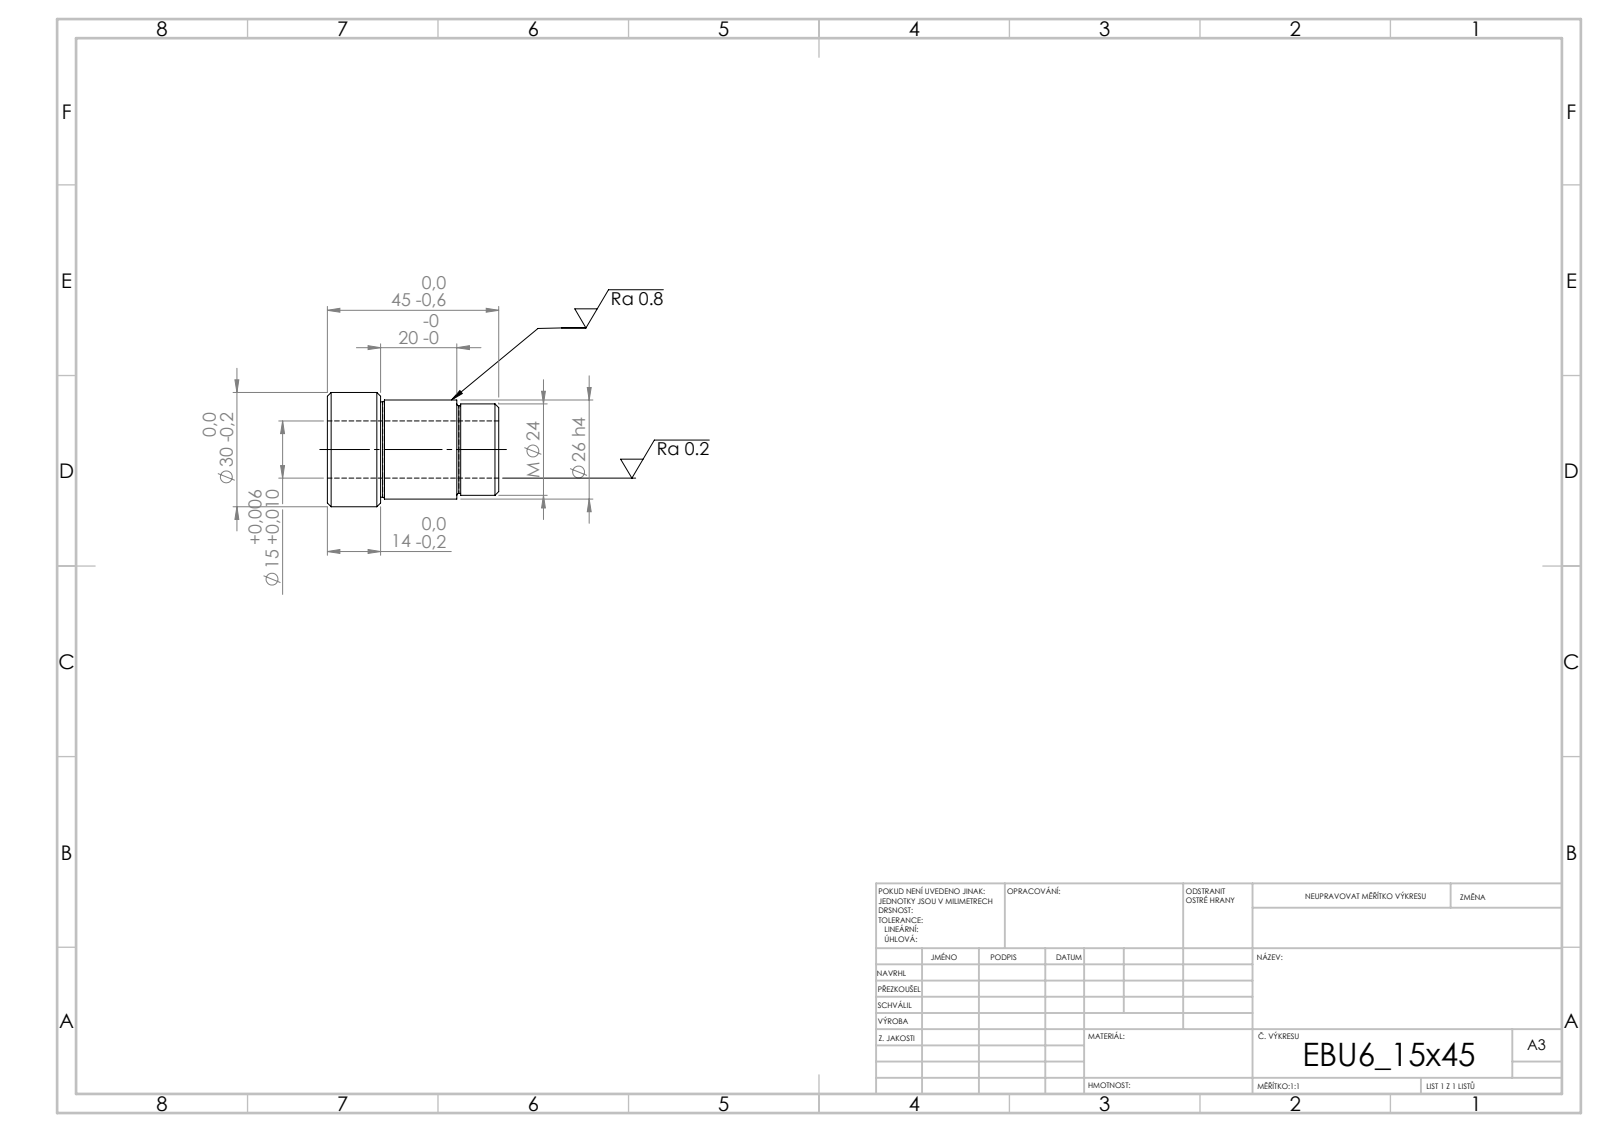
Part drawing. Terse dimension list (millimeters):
written by: SolidWorks 2019 (CONFIG_CONTROL_DESIGN)
unit: mm
bodies: 1 solid, 27 faces (5 planar, 12 cylindrical, 10 other)
size: 45 × 30 × 30
volume: 17 341 mm³; area: 6 920 mm²
holes: 1× ⌀15
bosses: 1× ⌀30, 1× ⌀26, 1× ⌀25, 1× ⌀24, 1× ⌀23
face distances: 45, 31, 14, 11, 20, 34, 10, 1, 21, 35
